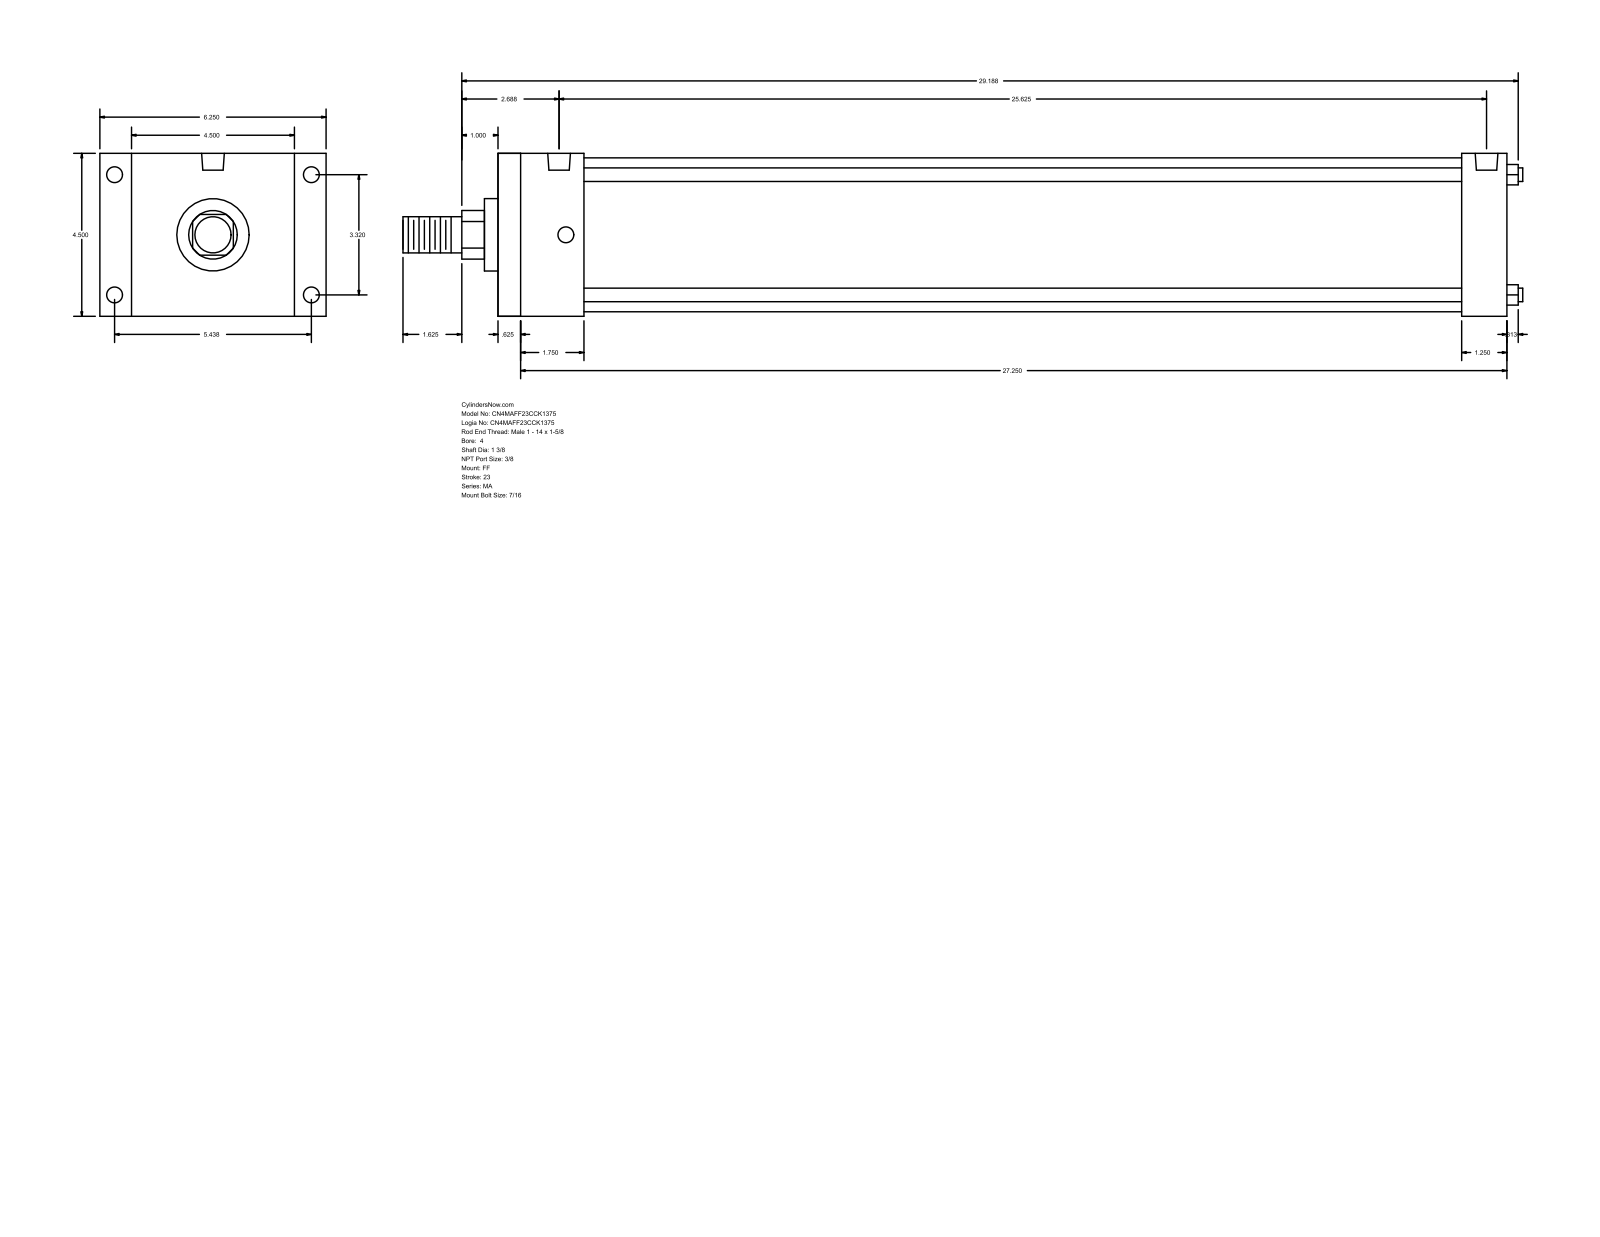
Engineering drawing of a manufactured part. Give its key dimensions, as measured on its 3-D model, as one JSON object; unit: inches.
{"part_name": "MA_FF__0400_1.375", "step_written_by": "GSSL Pune (CONFIG_CONTROL_DESIGN)", "units": "inches", "bodies": {"solids": 0, "faces": 92, "planar": 64, "cylindrical": 28, "other": 0}, "overall_size": [30.937, 6.25, 4.5], "round_holes": [[0.437, 8], [0.627, 2]], "round_bosses_or_shafts": [[0.375, 4], [4.25, 1], [2, 1], [1.375, 1], [1, 1]], "partial_cylinders_radius": [[0.672, 1]], "face_to_face_distances": [4.5, 27.875, 0.625, 27.25, 0.875, 5.375, 26.625, 26, 1.25, 2.375], "hole_center_spacings": [3.32, 5.438, 6.371, 25.25, 0.187, 0.188, 25.437, 25.438]}
